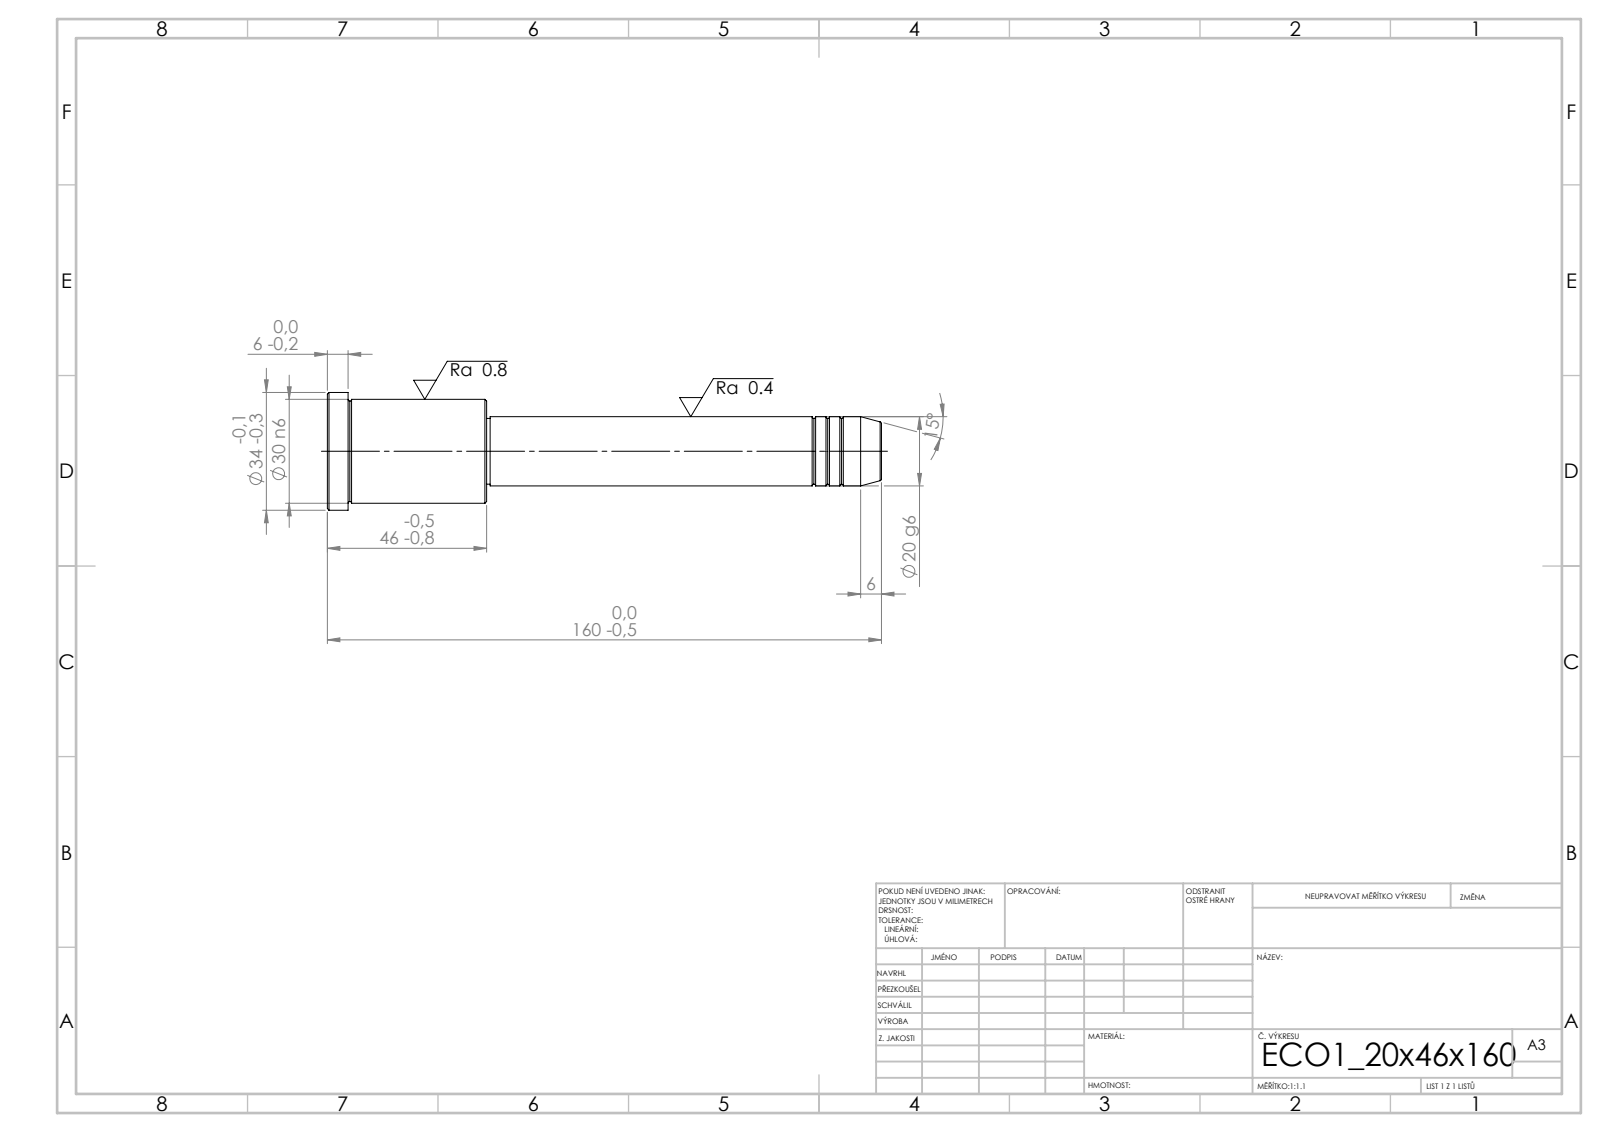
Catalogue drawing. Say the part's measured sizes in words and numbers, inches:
Its 3-D file was written by "SolidWorks 2019 (CONFIG_CONTROL_DESIGN)". It is 1 solid with 43 faces: 5 planar, 14 cylindrical and 24 other. Overall it measures 6.299 by 1.339 by 1.339 inches. Its volume is 4.216 cubic inches and its surface area 20.8 square inches. Round bosses or shafts: 1 of diameter 1.339, 1 of diameter 1.181, 1 of diameter 0.787, 1 of diameter 0.748. The main face-to-face distances are 1.811, 4.488, 6.299, 6.063, 1.575, 0.236, 4.449, 0.039, 1.614, 1.85.
